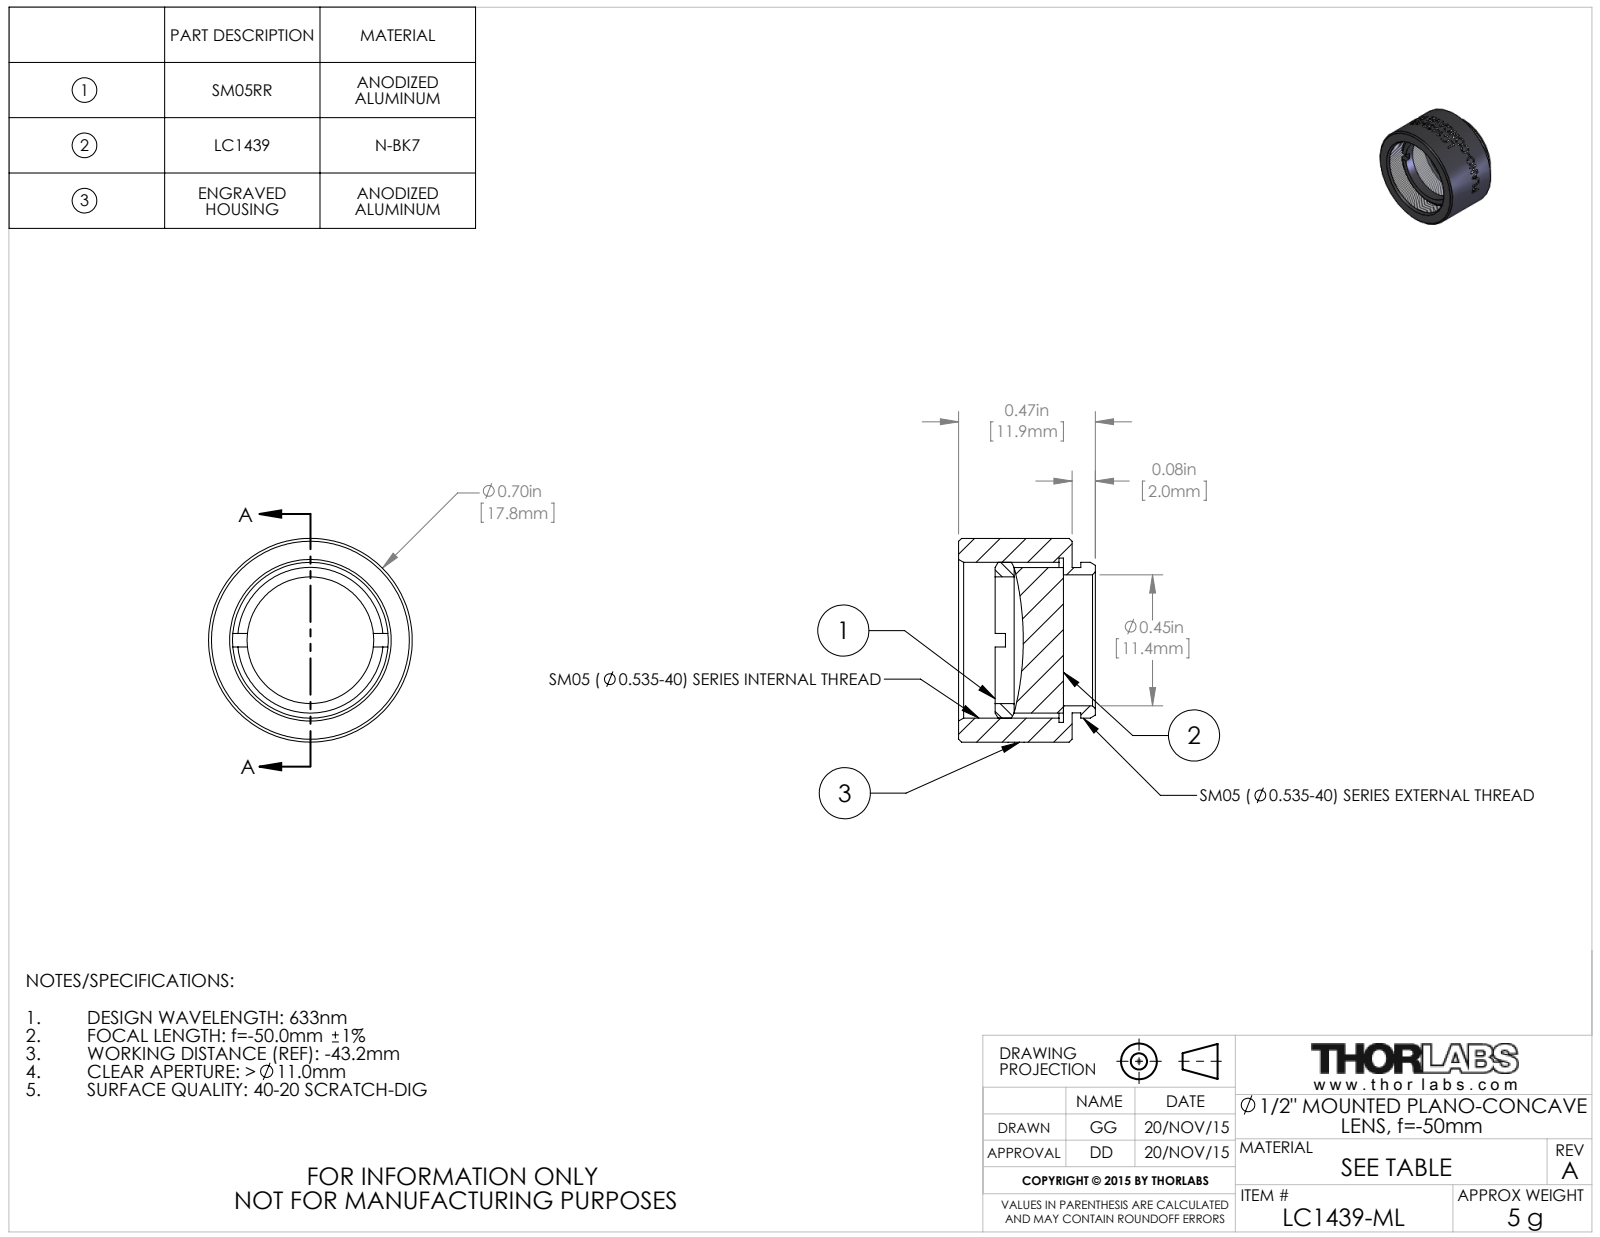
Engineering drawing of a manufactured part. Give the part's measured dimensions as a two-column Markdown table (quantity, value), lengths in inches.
| quantity | value |
| --- | --- |
| part name | TTN045257-E0W |
| STEP written by | SolidWorks 2014 (CONFIG_CONTROL_DESIGN) |
| units | inches |
| bodies | 3 solids, 110 faces (16 planar, 77 cylindrical, 17 other) |
| overall size | 0.7 × 0.7 × 0.47 |
| volume | 0.102 in³ |
| surface area | 3.242 in² |
| round holes (diameter × count) | 0.435 × 1, 0.45 × 1, 0.535 × 1, 0.565 × 1 |
| round bosses / shafts (diameter × count) | 0.7 × 1, 0.535 × 1, 0.5 × 1, 0.499 × 1 |
| main face-to-face distances | 0.03, 0.39, 0.36, 0.199, 0.169, 0.191, 0.264, 0.234, 0.065, 0.126 |
